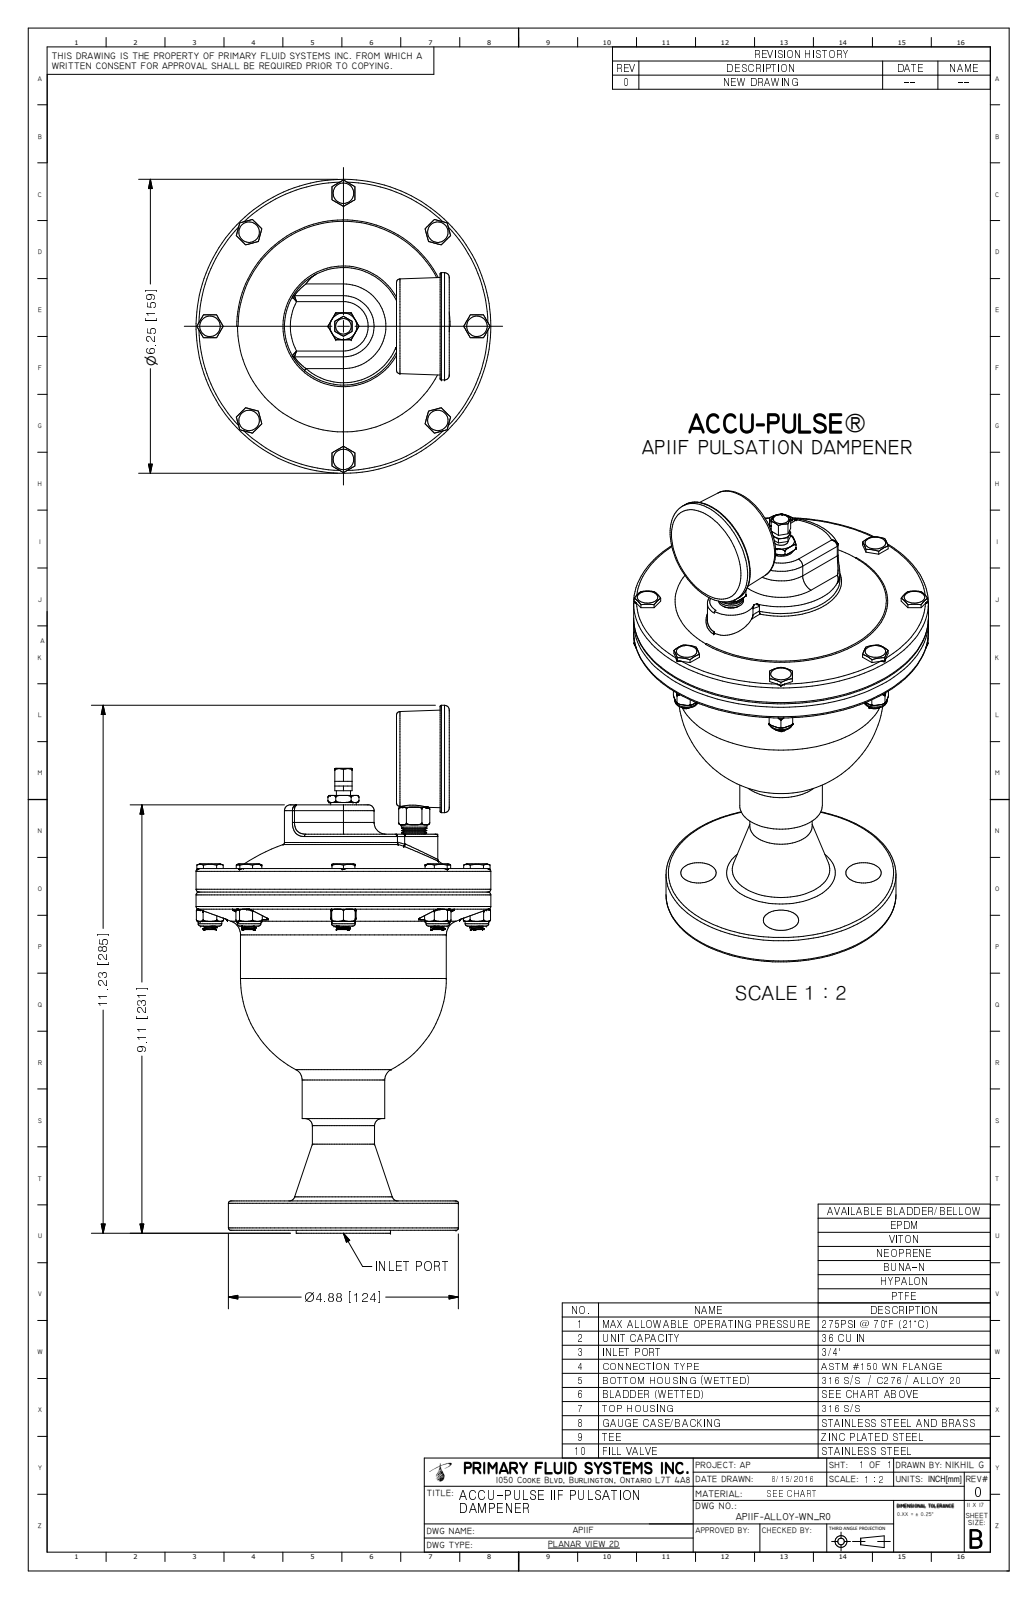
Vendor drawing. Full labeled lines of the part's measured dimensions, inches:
Part name (STEP PRODUCT): APIIF-ALLOY-WN_R0
STEP written by: Autodesk Inventor 2009 (AUTOMOTIVE_DESIGN)
Units: inches
Bodies: 12 solids, 709 faces (240 planar, 90 cylindrical, 379 other)
Overall size (bounding box): 11.225 × 6.25 × 6.25
Volume: 53.81 in³ · Surface area: 301.8 in²
Round holes (diameter × count): ⌀0.75 ×4, ⌀0.437 ×2, ⌀0.957 ×1, ⌀1.049 ×1, ⌀3.865 ×1
Round bosses / shafts (diameter × count): ⌀0.5 ×8, ⌀0.216 ×8, ⌀0.54 ×2, ⌀6.25 ×1, ⌀4.875 ×1, ⌀4.365 ×1, ⌀2.5 ×1, ⌀2.282 ×1
Partial cylindrical surfaces — rounded edges, fillets, slot ends (radius × count): R0.02 ×20, R0.1 ×16, R0.05 ×4, R0.125 ×2, R0.25 ×2, R0.5 ×1, R0.65 ×1
Main face-to-face distances: 0.625, 7.693, 7.068, 0.094, 0.013, 0.08, 8.422, 1.118, 1.104, 1.024
Hole centre spacings: 1.75, 2.475, 1.265, 3.004, 3.5, 1.5
